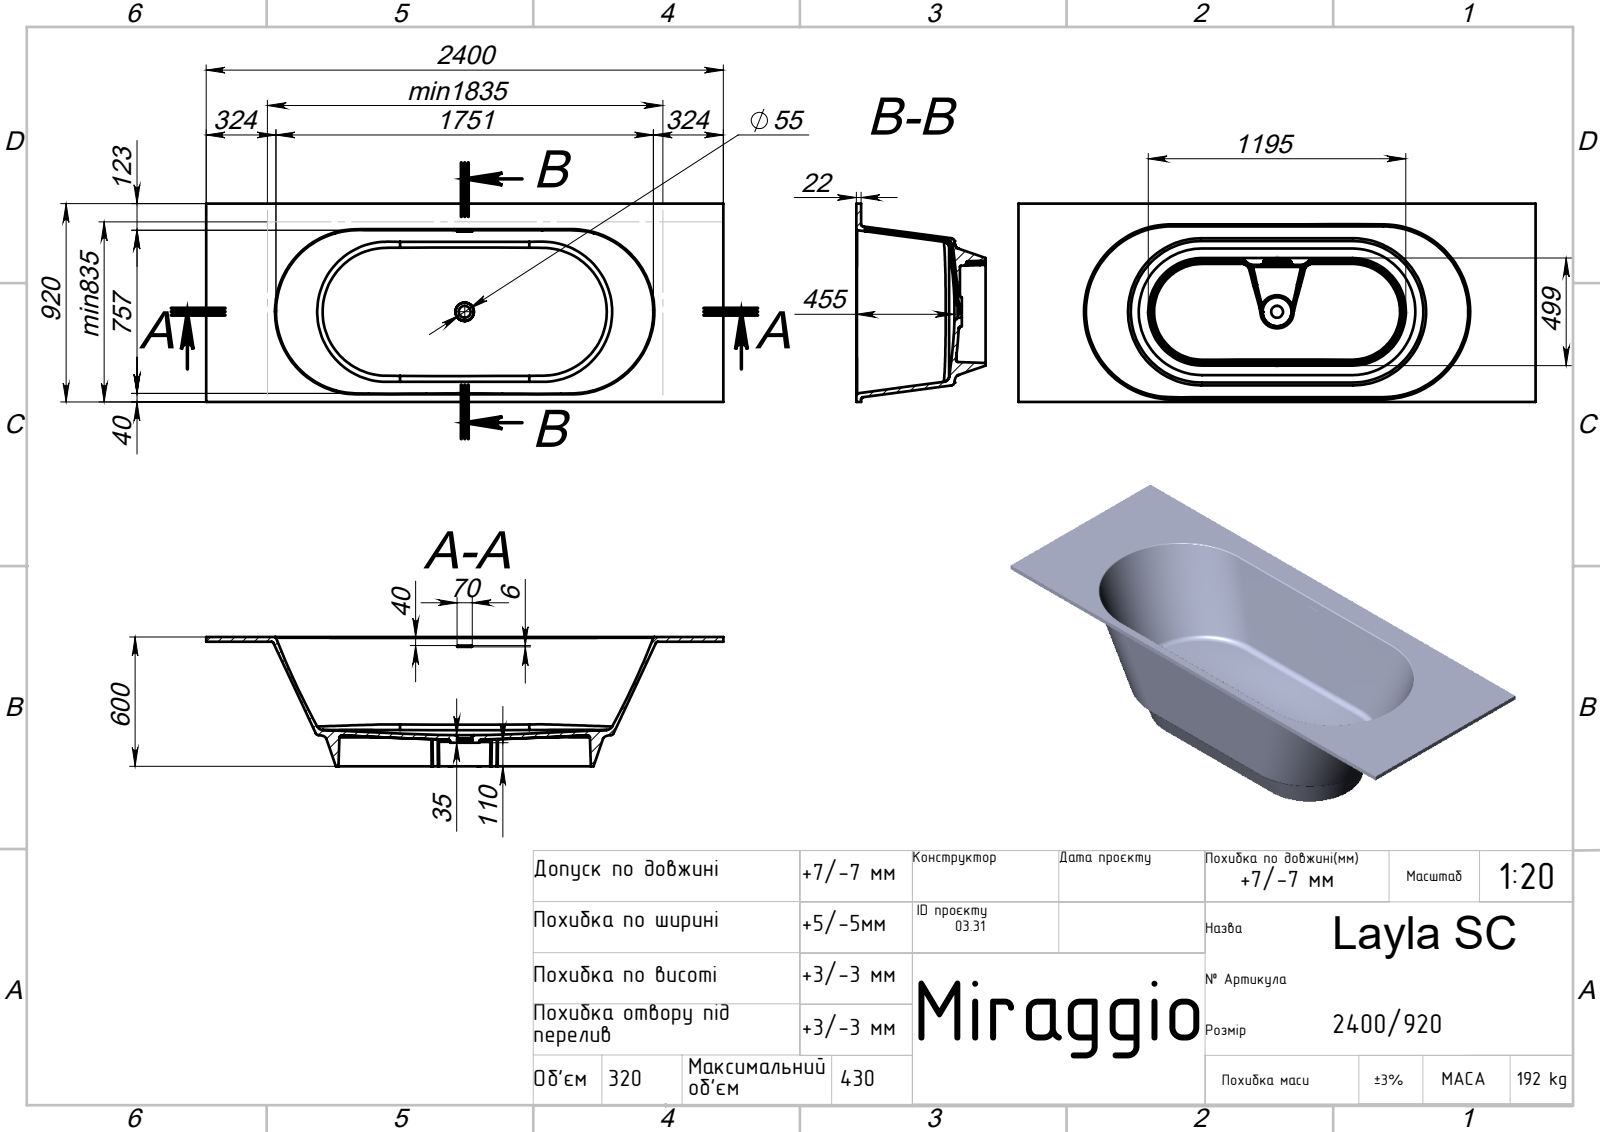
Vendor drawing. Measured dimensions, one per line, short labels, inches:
name: Layla SC
written by: SolidWorks 2020 (AUTOMOTIVE_DESIGN)
unit: in
bodies: 1 solid, 124 faces (28 planar, 18 cylindrical, 78 other)
size: 94.488 × 36.22 × 23.622
volume: 5 337 in³; area: 12 400 in²
holes: 1× ⌀2.165
rounds: 4× R0.394, 3× R0.197, 2× R0.118, 1× R1.457, 1× R1.811, 1× R2.461, 1× R7.818, 1× R9.341
face distances: 0.866, 36.22, 22.756, 23.622, 4.685, 18.071, 18.937, 94.488, 45.866, 48.622
